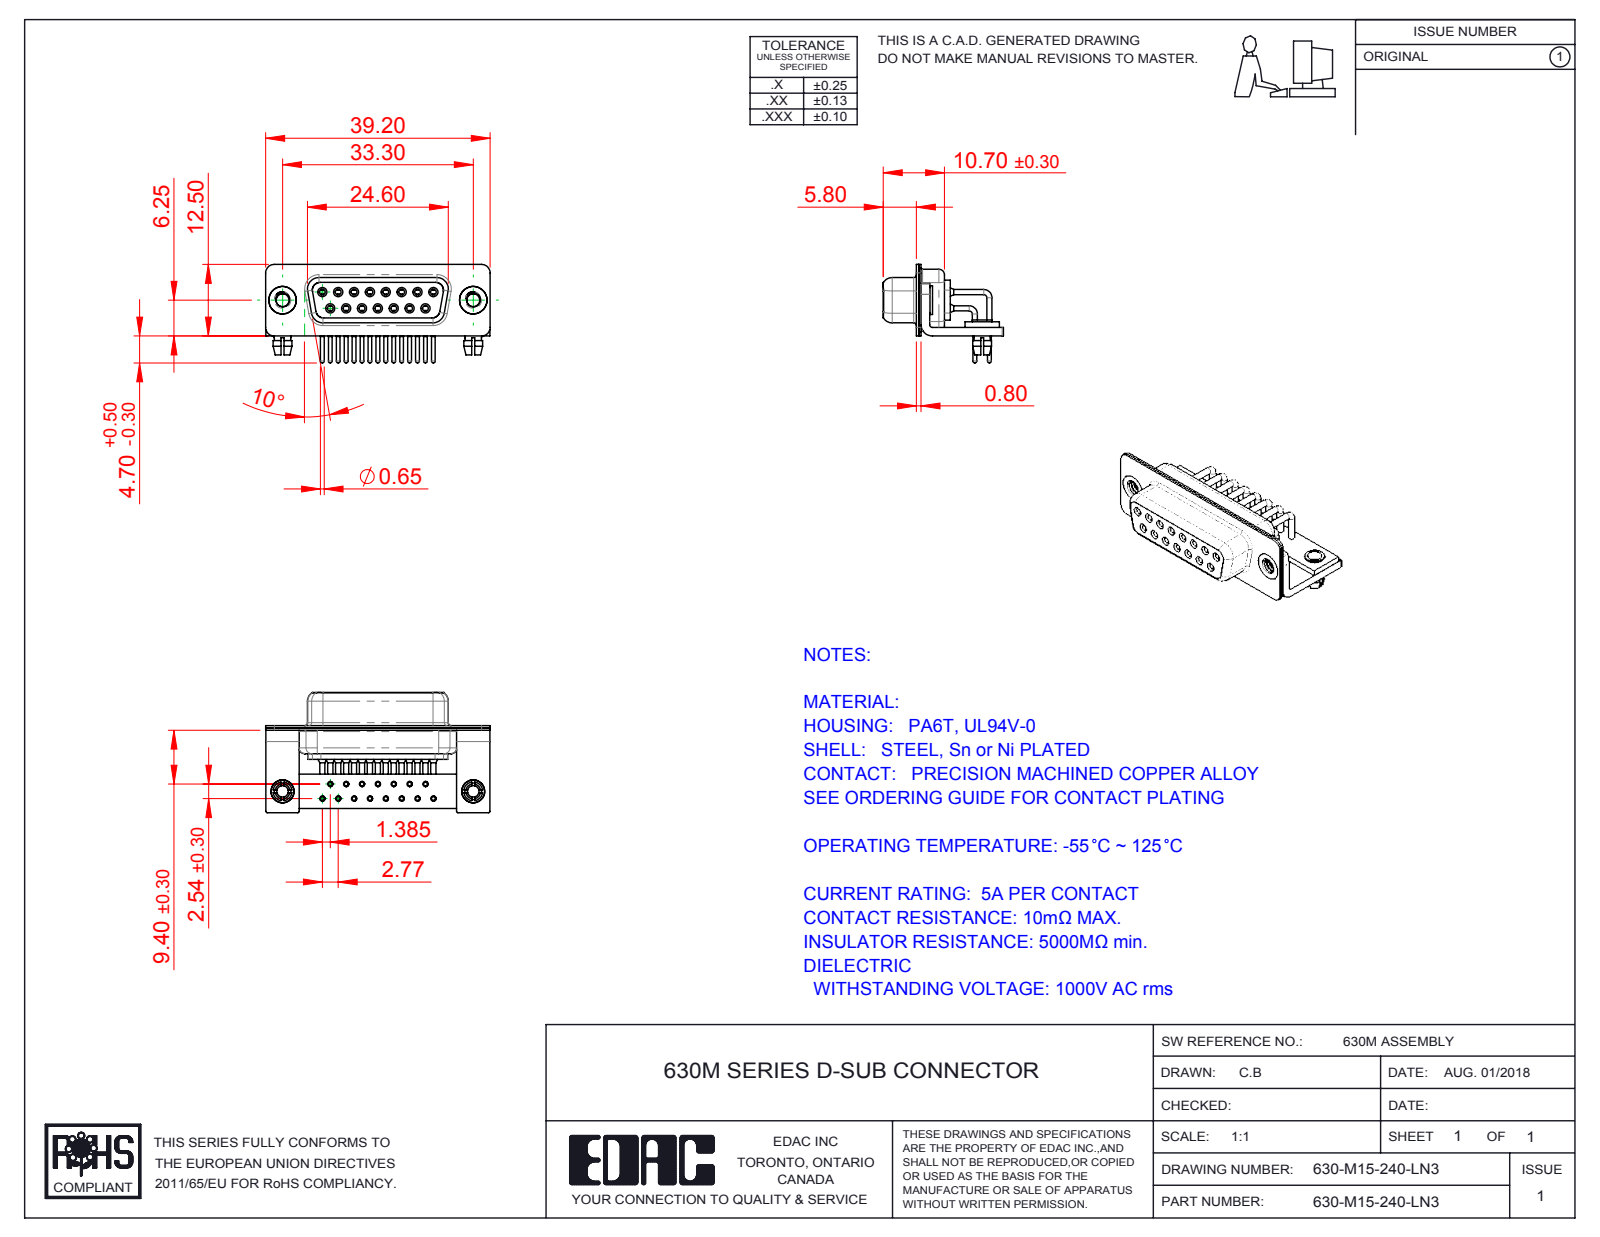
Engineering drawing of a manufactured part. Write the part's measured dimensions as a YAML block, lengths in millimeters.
part_name: "630M Shell Front_15 Contacts; 630M Contact Row 1; 630M Contact Row 2; 630M Shell Rear_15 Contacts (+6 more)"
step_written_by: "SolidWorks 2016 (CONFIG_CONTROL_DESIGN)"
units: millimeters
bodies: {solids: 25, faces: 1246, planar: 366, cylindrical: 566, other: 314}
overall_size: [39.2, 21, 17.2]
volume: 3090
surface_area: 7958
round_holes:
  - {diameter: 2, count: 17}
  - {diameter: 0.9, count: 15}
  - {diameter: 1, count: 15}
  - {diameter: 1.1, count: 15}
  - {diameter: 1.7, count: 15}
  - {diameter: 1.8, count: 15}
  - {diameter: 2.26, count: 2}
  - {diameter: 2.5, count: 2}
  - {diameter: 3.2, count: 2}
  - {diameter: 4, count: 2}
  - {diameter: 4.8, count: 2}
round_bosses_or_shafts:
  - {diameter: 0.9, count: 27}
  - {diameter: 1.6, count: 15}
  - {diameter: 1.5, count: 15}
  - {diameter: 0.65, count: 15}
  - {diameter: 5, count: 2}
  - {diameter: 4.9, count: 2}
  - {diameter: 4, count: 2}
  - {diameter: 3.4, count: 2}
partial_cylinders:
  - {radius: 0.25, count: 16}
  - {radius: 1.5, count: 16}
  - {radius: 2, count: 13}
  - {radius: 1.35, count: 8}
  - {radius: 1.6, count: 8}
  - {radius: 0.5, count: 5}
  - {radius: 0.6, count: 4}
  - {radius: 0.65, count: 4}
face_to_face_distances: [0.4, 0.8, 2.3, 1.5, 9.35, 1.9, 1, 1.45, 8.95, 0.85]
hole_center_spacings: [2.77, 5.54, 8.31, 3.16, 4.87, 11.08, 2.89, 7.37]
